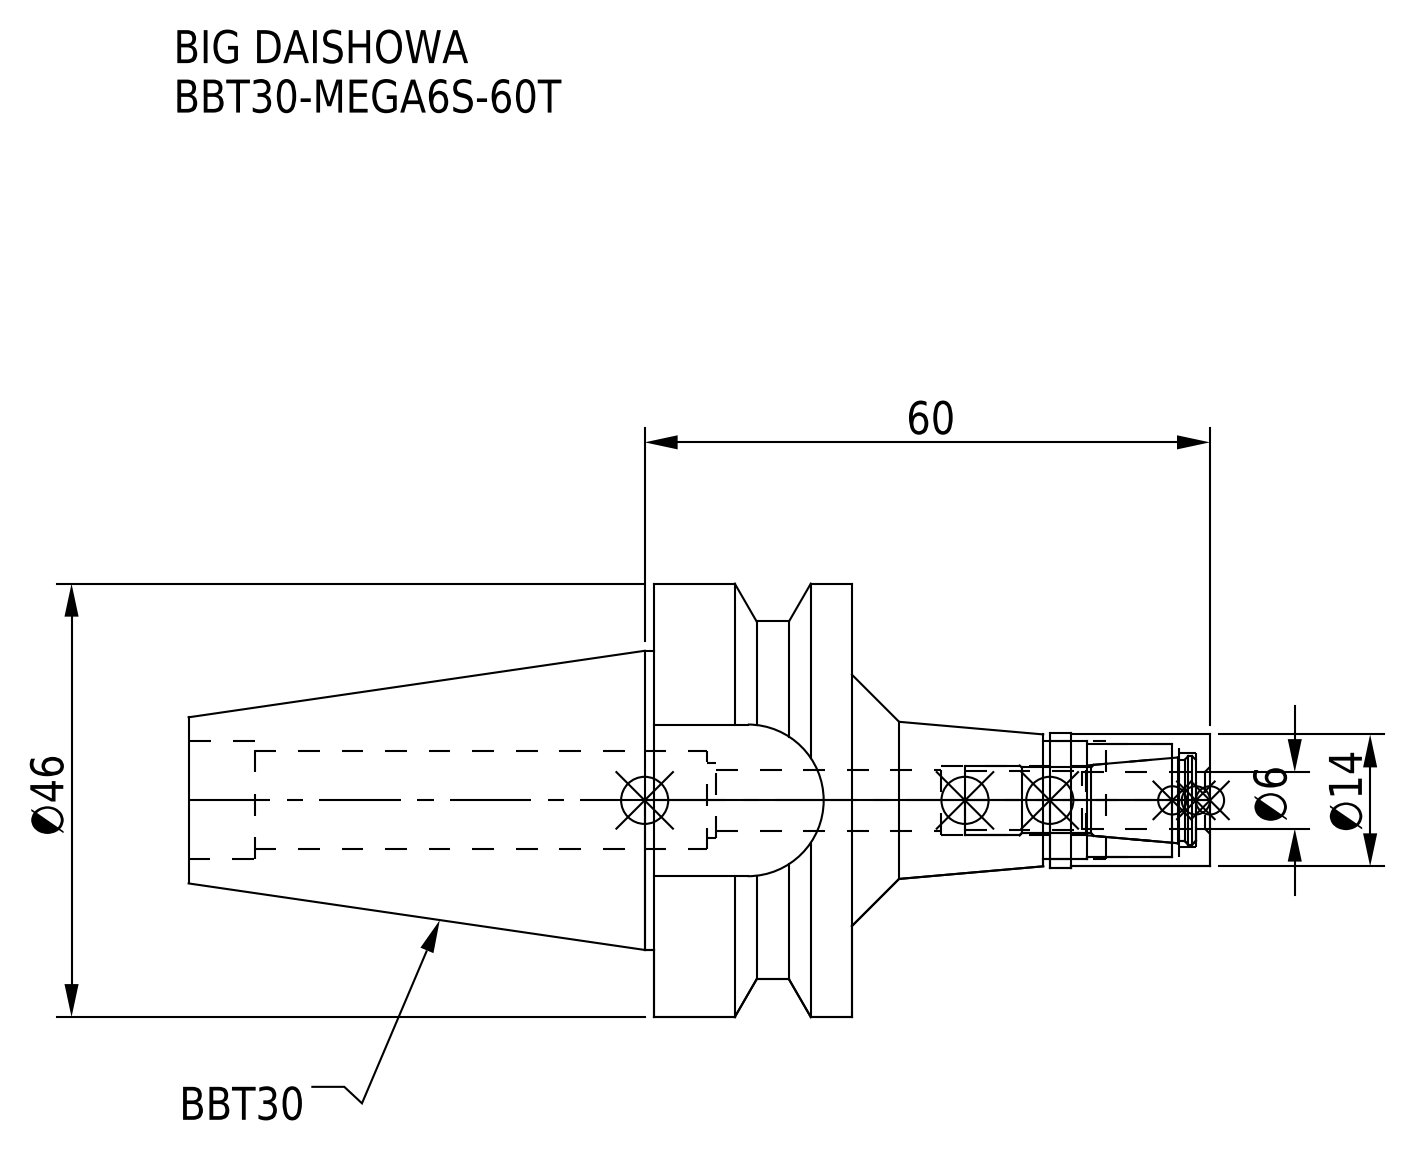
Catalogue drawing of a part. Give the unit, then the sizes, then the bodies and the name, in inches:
Units: inches
Overall size (bounding box): 4.268 × 1.811 × 1.811
Round holes (diameter × count): ⌀0.24 ×1, ⌀0.252 ×1, ⌀0.291 ×1, ⌀0.315 ×1, ⌀0.394 ×1, ⌀0.409 ×1, ⌀0.472 ×1, ⌀0.492 ×1
Round bosses / shafts (diameter × count): ⌀1.811 ×1, ⌀1.25 ×1, ⌀0.563 ×1, ⌀0.551 ×1
Partial cylindrical surfaces — rounded edges, fillets, slot ends (radius × count): R0.317 ×1, R0.748 ×1
Main face-to-face distances: 0.827, 1.283, 1.945, 2.772, 1.496, 2.323, 4.268, 0.634, 2.165, 0.028
Volume: 3.3 in³ · Surface area: 24.87 in²
Bodies: 2 solids, 74 faces (22 planar, 38 cylindrical, 14 other)
Part name (STEP PRODUCT): BBT30-MEGA6S-60T; BBT30-MEGA6S-60T-FreeParts; BBT30-MEGA6S-60T_1.stp; DXF_TEMP_ASSY_ASM_4_ASM.stp (+3 more)
STEP written by: SolidWorks 2019 (CONFIG_CONTROL_DESIGN)
